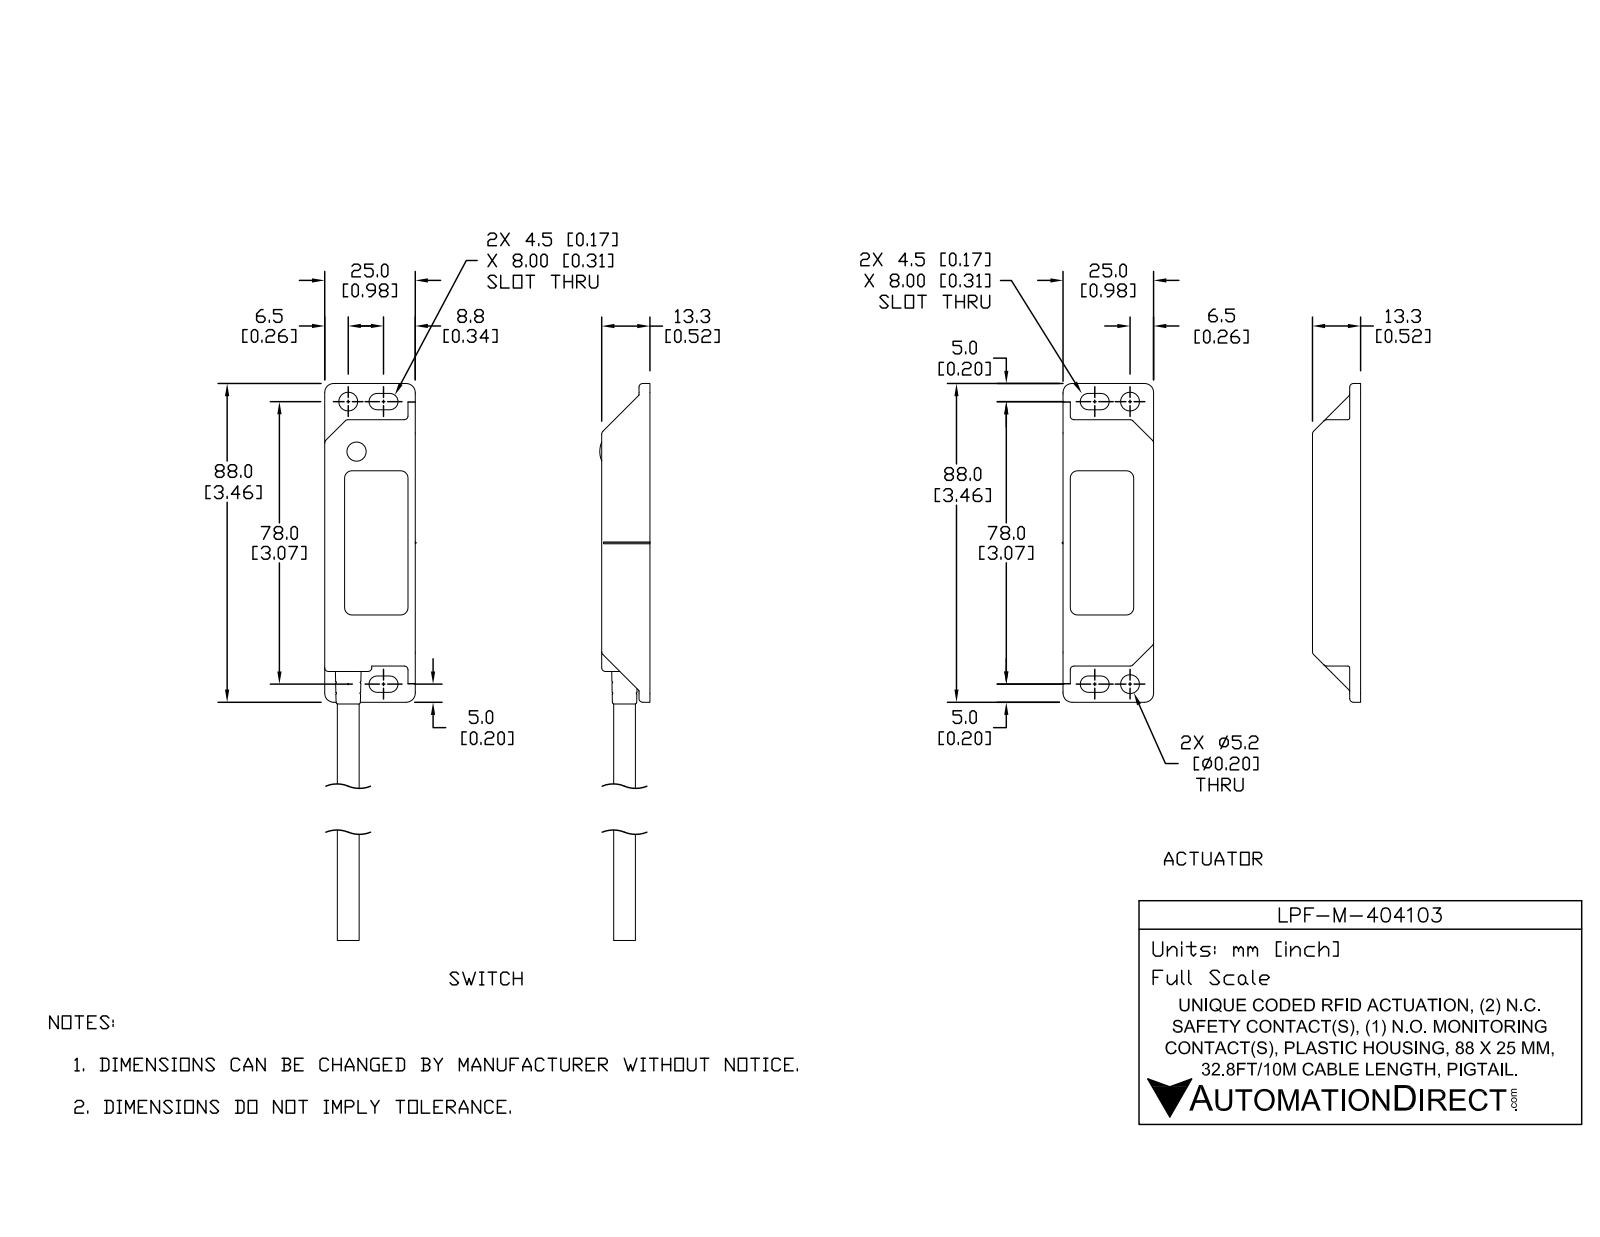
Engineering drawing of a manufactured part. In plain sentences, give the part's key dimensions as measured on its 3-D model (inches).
The part is named "LPF-M-404103; LPF-M-404103_1; LPF-M-404103_2". Its 3-D file was written by "SolidWorks 2017 (AUTOMOTIVE_DESIGN)". It is 11 solids with 1058 faces: 401 planar, 303 cylindrical and 354 other. Overall it measures 8.849 by 1.992 by 0.543 inches. Its volume is 1.638 cubic inches and its surface area 46.88 square inches. Round holes: 4 of diameter 0.197, 4 of diameter 0.205, 1 of diameter 0.119, 1 of diameter 0.173, 1 of diameter 0.213, 1 of diameter 0.232, 1 of diameter 0.276. Round bosses or shafts: 4 of diameter 0.079, 2 of diameter 0.193, 2 of diameter 0.091, 1 of diameter 0.339, 1 of diameter 0.299, 1 of diameter 0.28, 1 of diameter 0.236, 1 of diameter 0.209. Partial cylindrical surfaces (rounded edges, fillets, slot ends): 116 of radius 0.02, 49 of radius 0.039, 10 of radius 0.079, 8 of radius 0.089, 8 of radius 0.098, 6 of radius 0.012, 1 of radius 0.189. The main face-to-face distances are 0.067, 0.441, 0.079, 0.374, 0.059, 0.071, 0.508, 0.445, 0.512, 0.988. The hole center spacings are 0.748, 1.097, 1.19, 1.275, 1.48, 1.571, 1.784, 1.895.
